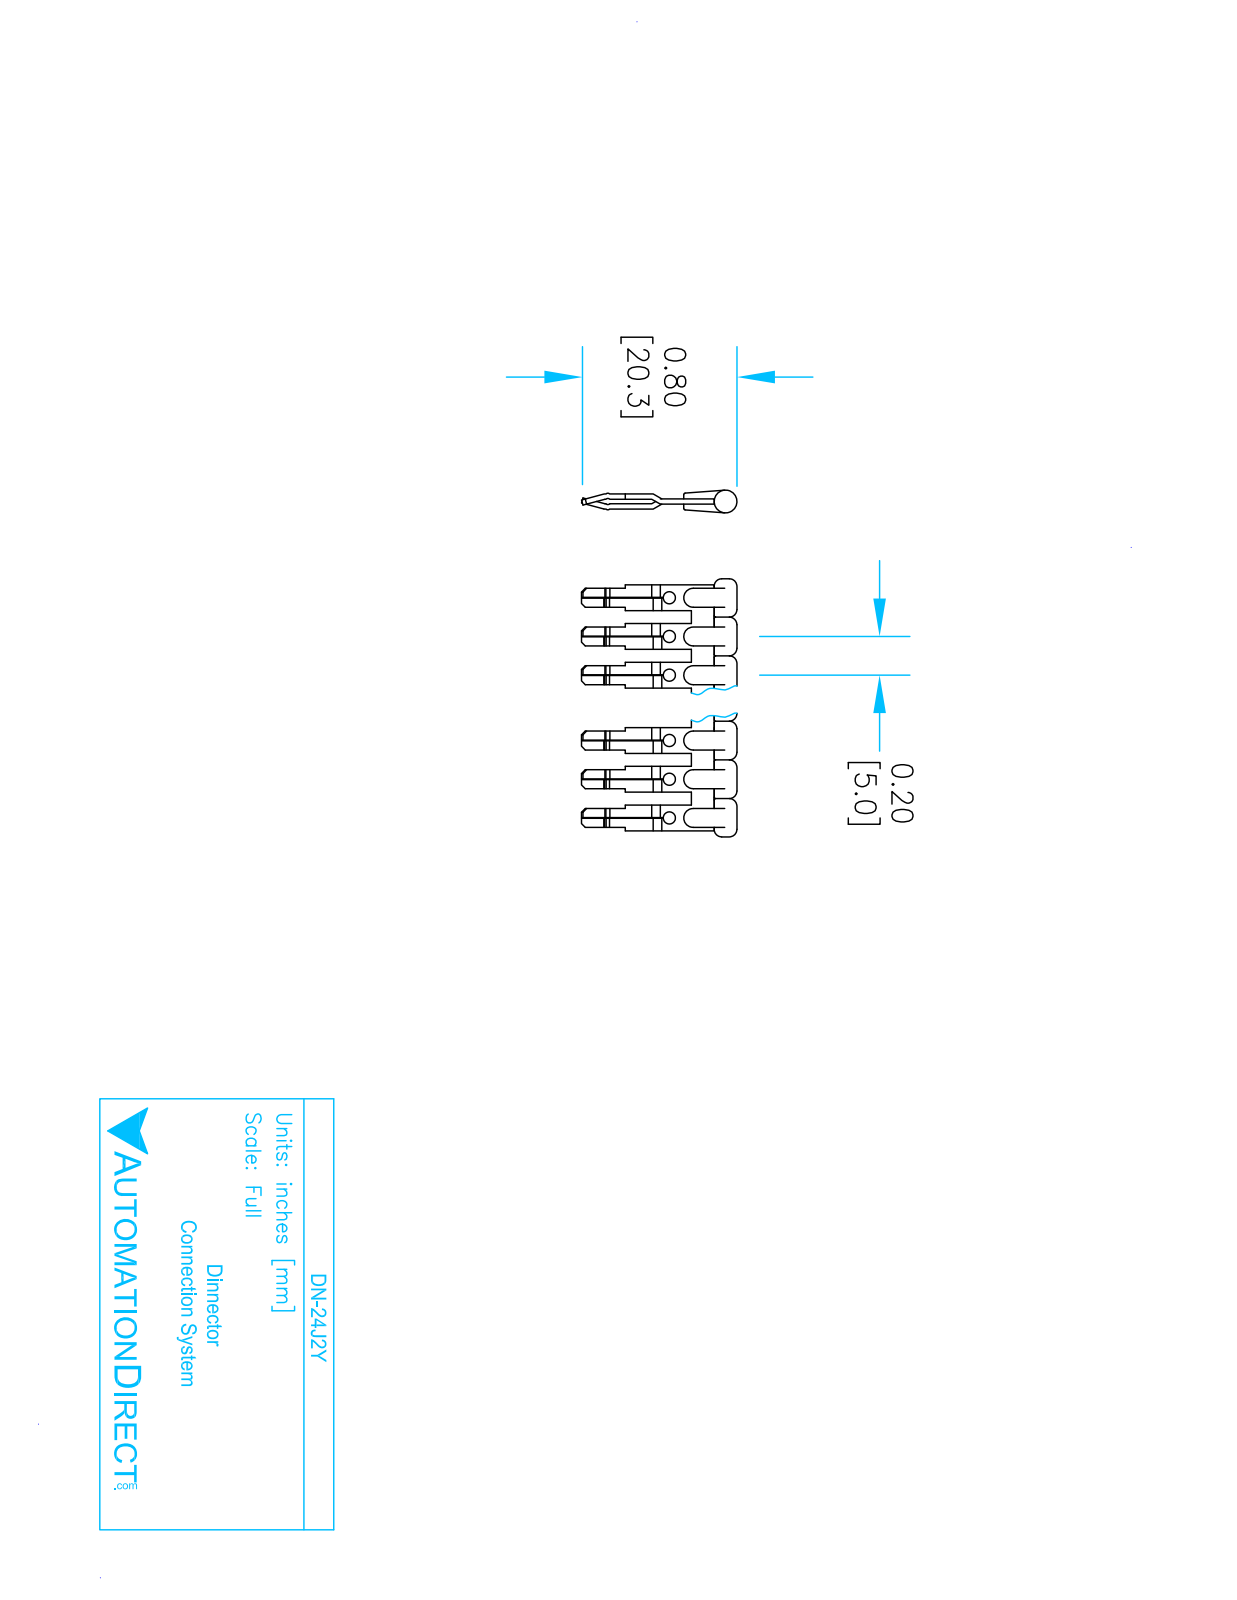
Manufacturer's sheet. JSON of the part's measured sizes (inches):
{"part_name": "J2,5PSX_J4 INTERMEDIO; J2,5_M; J2,5_N; 43525_24_DN-24J2Y (+1 more)", "step_written_by": "SolidWorks 2013 (AUTOMOTIVE_DESIGN)", "units": "inches", "bodies": {"solids": 48, "faces": 1822, "planar": 1090, "cylindrical": 472, "other": 260}, "overall_size": [4.815, 0.801, 0.125], "volume_in3": 0.143, "surface_area_in2": 9.641, "round_holes": [[0.051, 48]], "round_bosses_or_shafts": [[0.118, 1]], "partial_cylinders_radius": [[0.02, 96], [0.049, 24], [0.028, 4], [0.03, 1]], "face_to_face_distances": [0.028, 0.022, 0.049, 0.043, 0.071, 0.016, 0.201, 0.402, 0.602, 0.803], "hole_center_spacings": [0.201, 0.258, 0.402, 0.433, 0.602, 0.624, 0.803, 0.819]}
